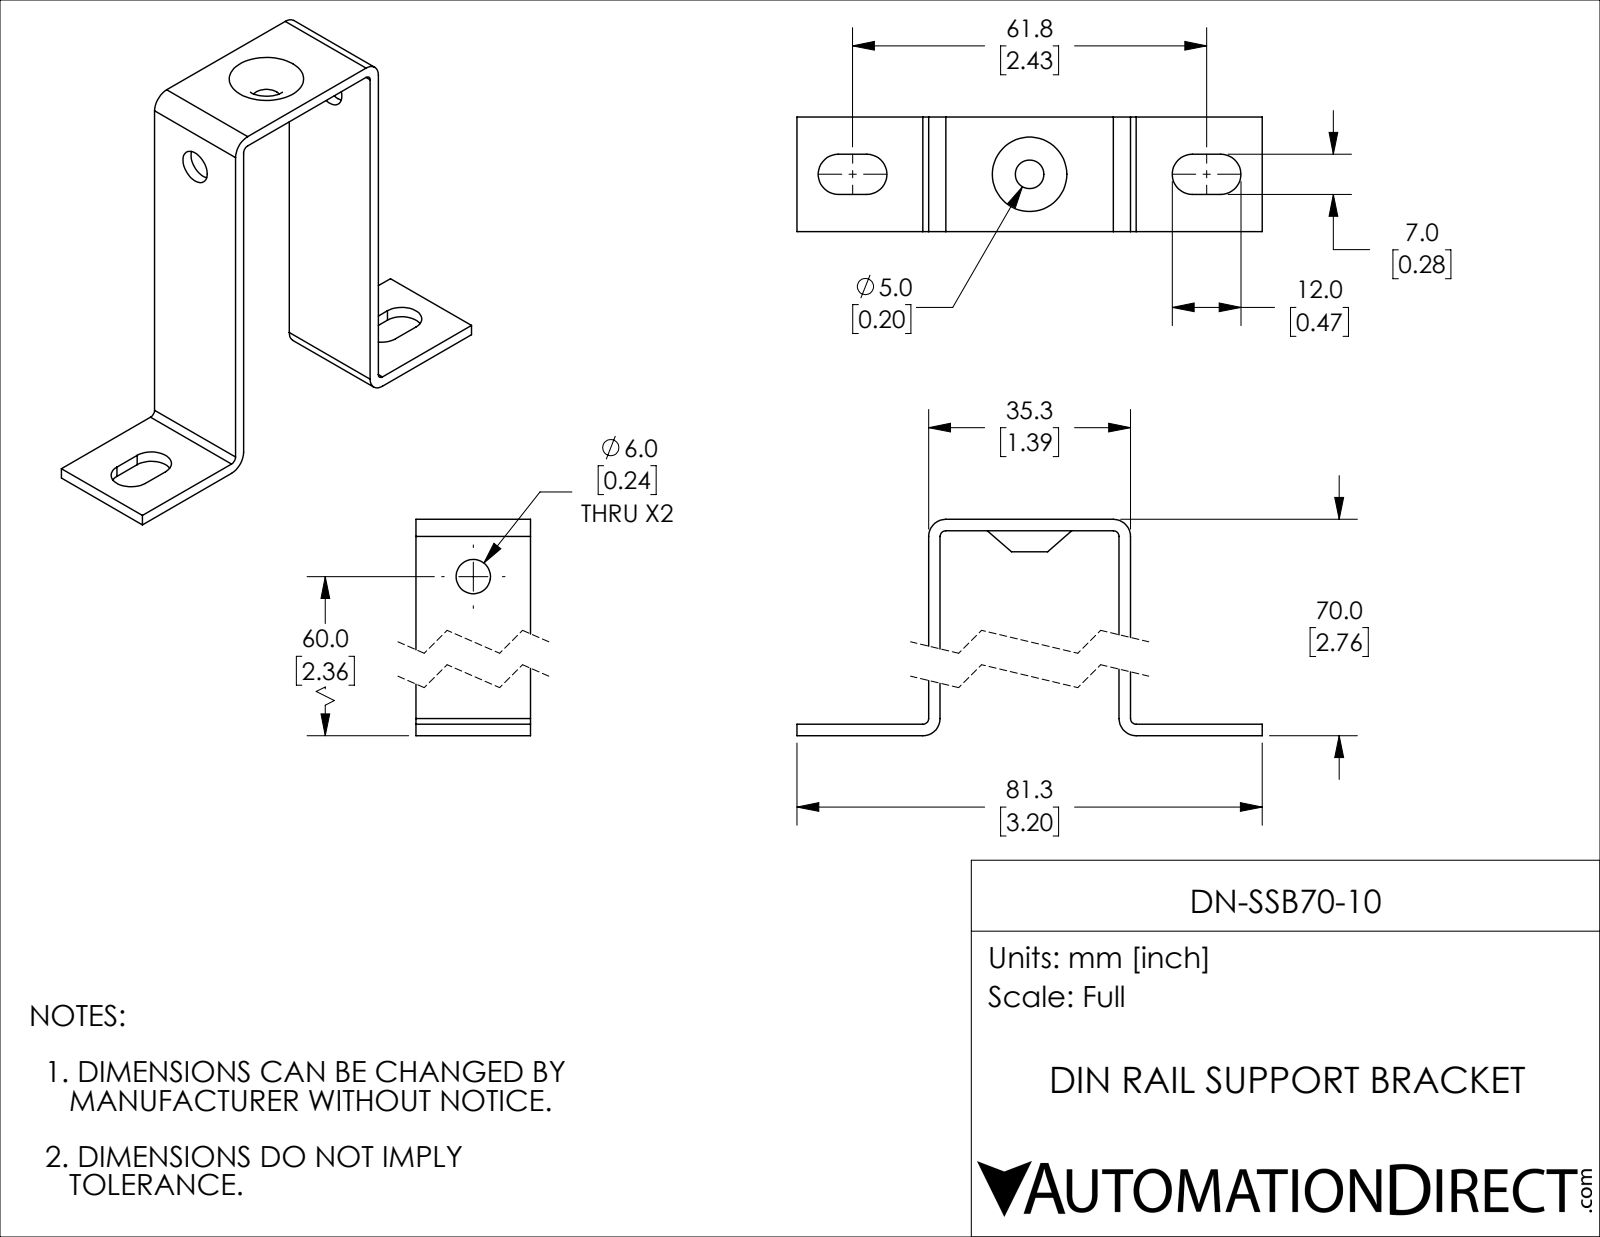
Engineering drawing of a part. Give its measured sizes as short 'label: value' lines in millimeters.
name: DN-SSB70-10
written by: SolidWorks 2018 (AUTOMOTIVE_DESIGN)
unit: mm
bodies: 1 solid, 43 faces (19 planar, 20 cylindrical, 4 other)
size: 81.25 × 70 × 20
volume: 8 298 mm³; area: 9 359 mm²
holes: 1× ⌀5, 1× ⌀6
rounds: 4× R1, 4× R3, 4× R3.5
face distances: 2, 33.24, 35.24, 31.24, 68, 70, 20, 66, 23, 25
